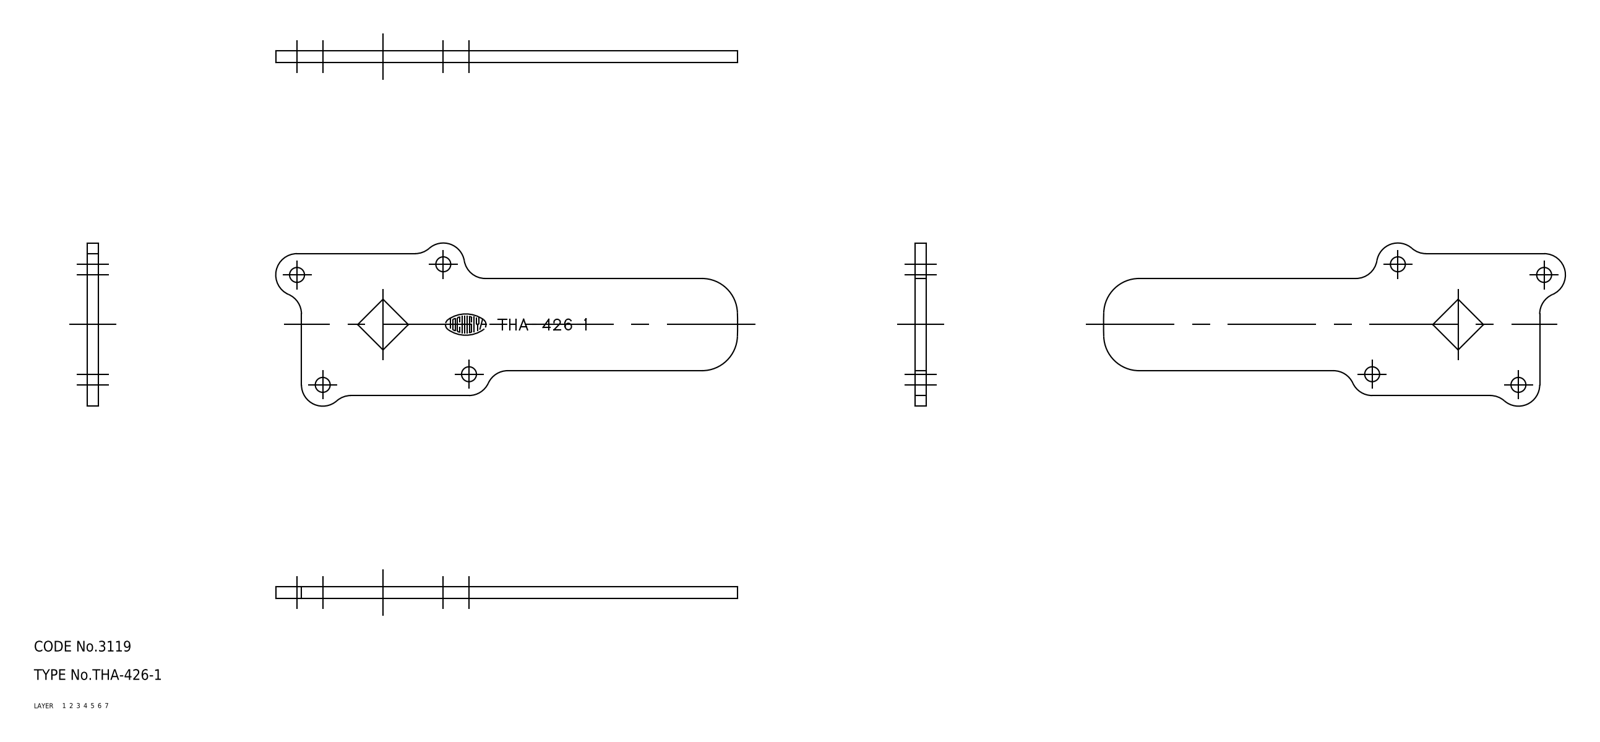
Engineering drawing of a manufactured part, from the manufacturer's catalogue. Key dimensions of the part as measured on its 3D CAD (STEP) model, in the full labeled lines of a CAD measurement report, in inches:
Part name (STEP PRODUCT): cam
STEP written by: CADfix (AUTOMOTIVE_DESIGN)
Units: inches
Bodies: 1 solid, 31 faces (0 planar, 0 cylindrical, 31 other)
Overall size (bounding box): 5.128 × 1.811 × 0.126
Volume: 0.745 in³ · Surface area: 13.88 in²
